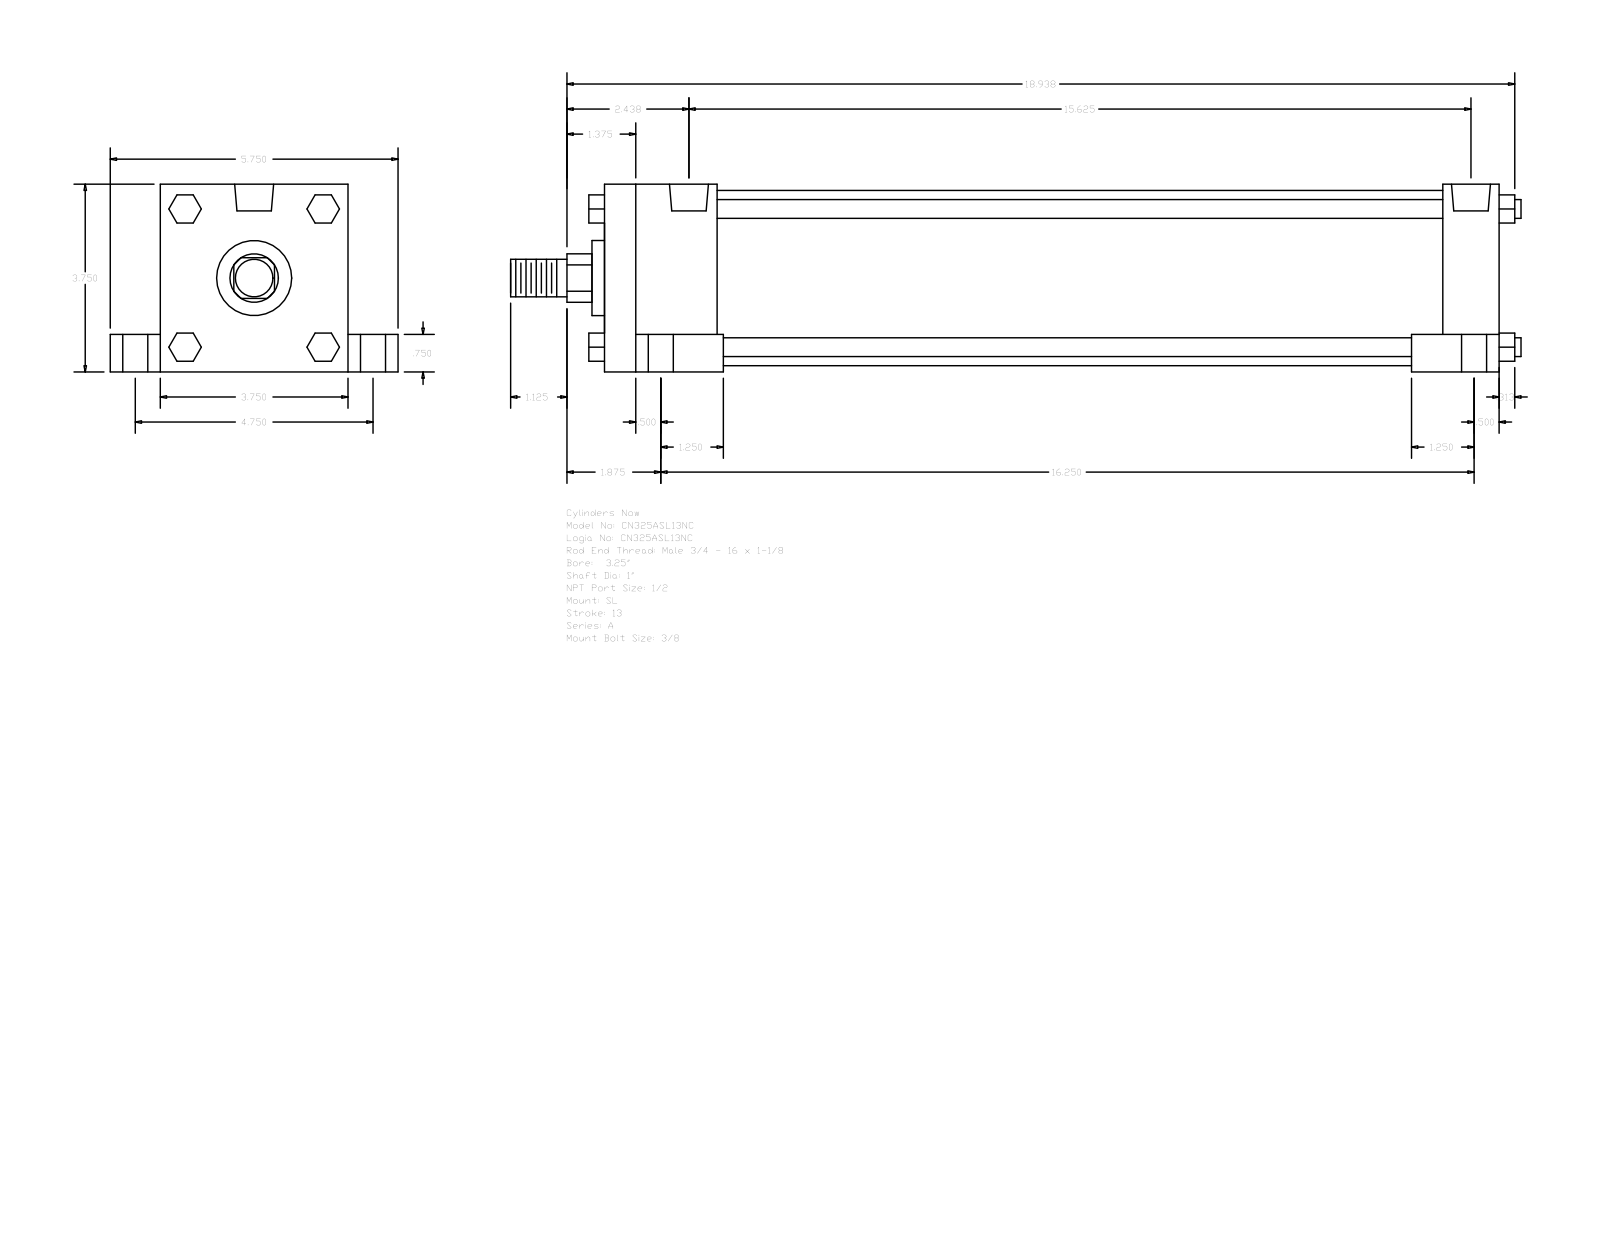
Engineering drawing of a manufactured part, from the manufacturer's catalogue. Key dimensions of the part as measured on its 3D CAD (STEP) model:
Part name (STEP PRODUCT): A_SL__0325_1
STEP written by: GSSL Pune (CONFIG_CONTROL_DESIGN)
Units: millimetres
Bodies: 0 solids, 150 faces (114 planar, 36 cylindrical, 0 other)
Overall size (bounding box): 512.76 × 146.05 × 95.25
Round holes (diameter × count): ⌀8.73 ×4, ⌀12.7 ×4, ⌀19.05 ×4, ⌀19.77 ×2
Round bosses / shafts (diameter × count): ⌀9.53 ×4, ⌀88.9 ×1, ⌀38.1 ×1, ⌀25.4 ×1, ⌀19.05 ×1
Partial cylindrical surfaces — rounded edges, fillets, slot ends (radius × count): R12.29 ×1
Main face-to-face distances: 95.24, 454.02, 19.05, 25.41, 120.65, 76.19, 28.57, 57.15, 425.45, 368.3
Hole centre spacings: 3.18, 60.35, 60.52, 62, 62.81, 120.66, 390.52, 393.7
